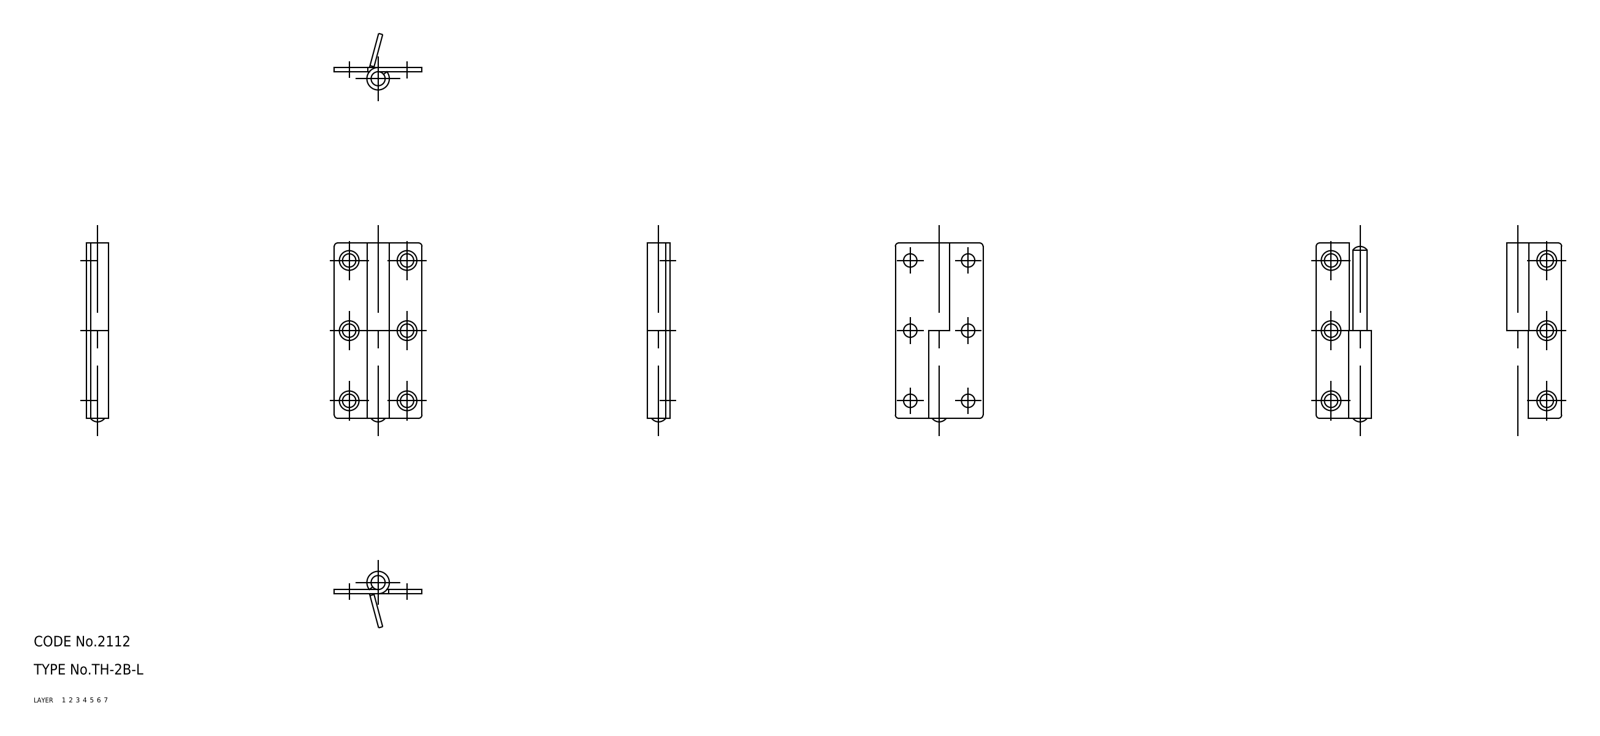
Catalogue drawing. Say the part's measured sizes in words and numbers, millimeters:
The part is named "shaft; hinge piece_B; hinge piece_A; TH_2B_L_7253_36". Its 3-D file was written by "CADfix (AUTOMOTIVE_DESIGN)". It is 3 solids with 52 faces: 0 planar, 0 cylindrical and 52 other. Overall it measures 51 by 25 by 6.4 millimeters. Its volume is 2 659 cubic millimeters and its surface area 4 513 square millimeters.
